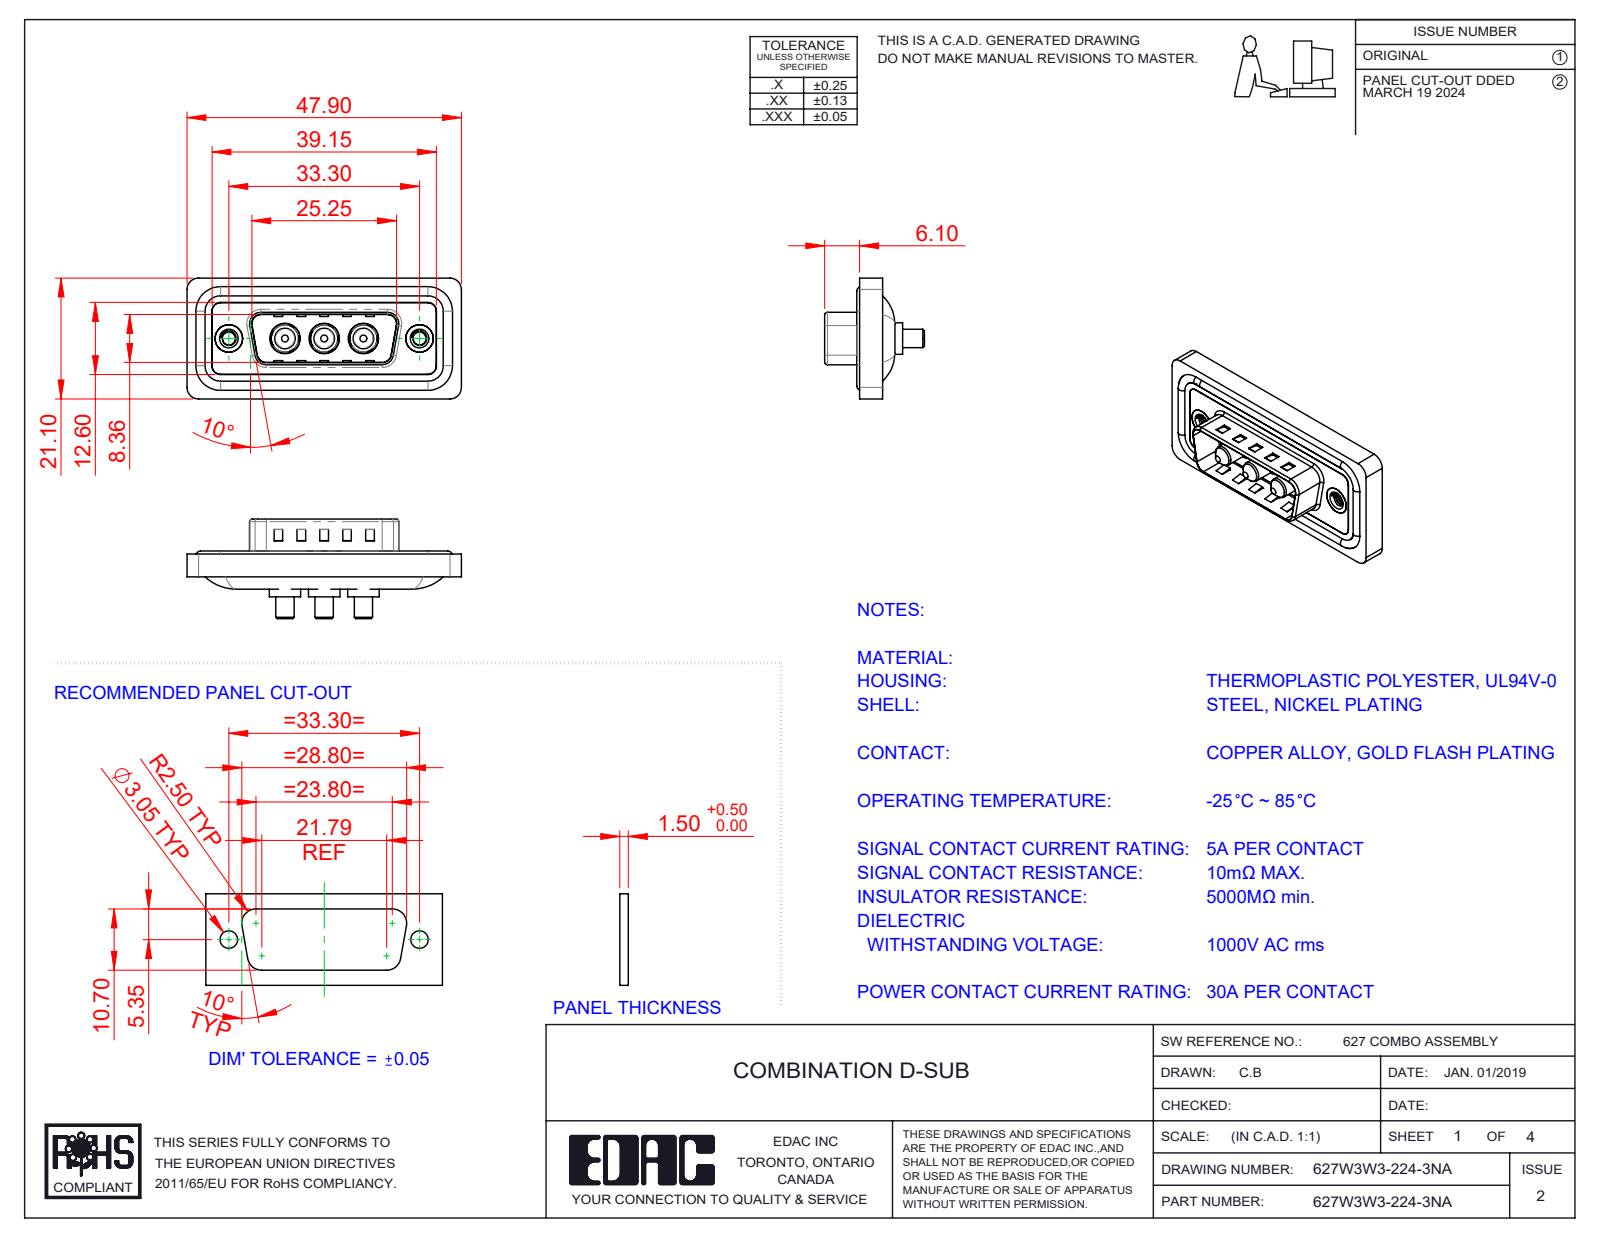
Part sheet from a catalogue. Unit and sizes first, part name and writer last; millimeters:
Units: millimetres
Overall size (bounding box): 47.9 × 21.1 × 17.4
Round holes (diameter × count): ⌀4.85 ×3, ⌀5.3 ×3, ⌀2.26 ×2, ⌀4 ×2, ⌀4.8 ×2, ⌀5 ×2
Round bosses / shafts (diameter × count): ⌀1.6 ×4, ⌀5.5 ×3, ⌀5.2 ×3, ⌀4.75 ×3, ⌀3.75 ×3, ⌀3.6 ×3, ⌀3.2 ×3, ⌀4.9 ×2
Partial cylindrical surfaces — rounded edges, fillets, slot ends (radius × count): R1.5 ×26, R2 ×20, R0.5 ×8, R1.6 ×8, R0.25 ×4, R0.6 ×4, R0.65 ×4, R0.9 ×4
Main face-to-face distances: 0.4, 1.1, 1.5, 0.5, 1.6, 3.1, 2.9, 4, 0.82, 9.58
Hole centre spacings: 6.85, 9.8, 16.65, 23.5, 13.7, 33.3
Volume: 5 609 mm³ · Surface area: 8 765 mm²
Bodies: 13 solids, 562 faces (207 planar, 243 cylindrical, 112 other)
Part name (STEP PRODUCT): 627Combo Shell Rear_15 Contacts; 627Combo Waterproof Housing_15 Contacts; 627Combo Housing_3W3; Power Pin_30A S (+3 more)
STEP written by: SolidWorks 2023 (CONFIG_CONTROL_DESIGN)
